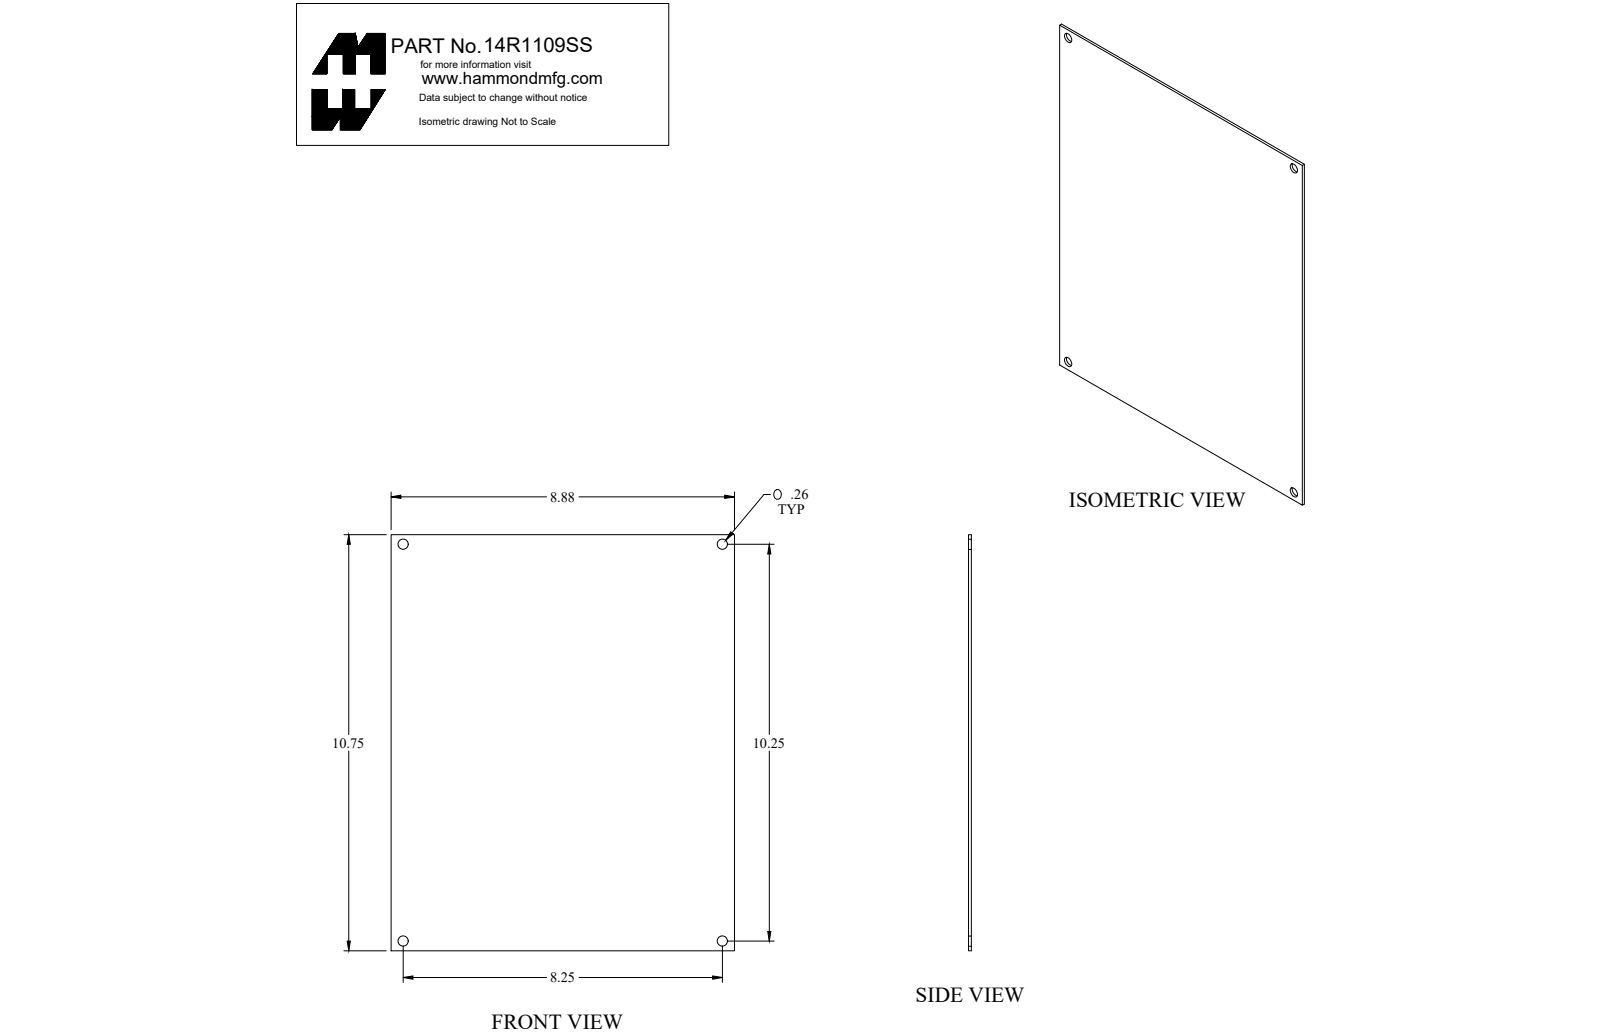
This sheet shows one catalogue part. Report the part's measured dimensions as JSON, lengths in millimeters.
{"part_name": "14R1109SS", "step_written_by": "SolidWorks 2018 (AUTOMOTIVE_DESIGN)", "units": "millimeters", "bodies": {"solids": 1, "faces": 10, "planar": 6, "cylindrical": 4, "other": 0}, "overall_size": [273.1, 225.4, 1.8], "volume_mm3": 112300, "surface_area_mm2": 124800, "round_holes": [[6.7, 4]], "face_to_face_distances": [1.8, 225.4, 273.1], "hole_center_spacings": [209.6, 260.4, 334.2]}
